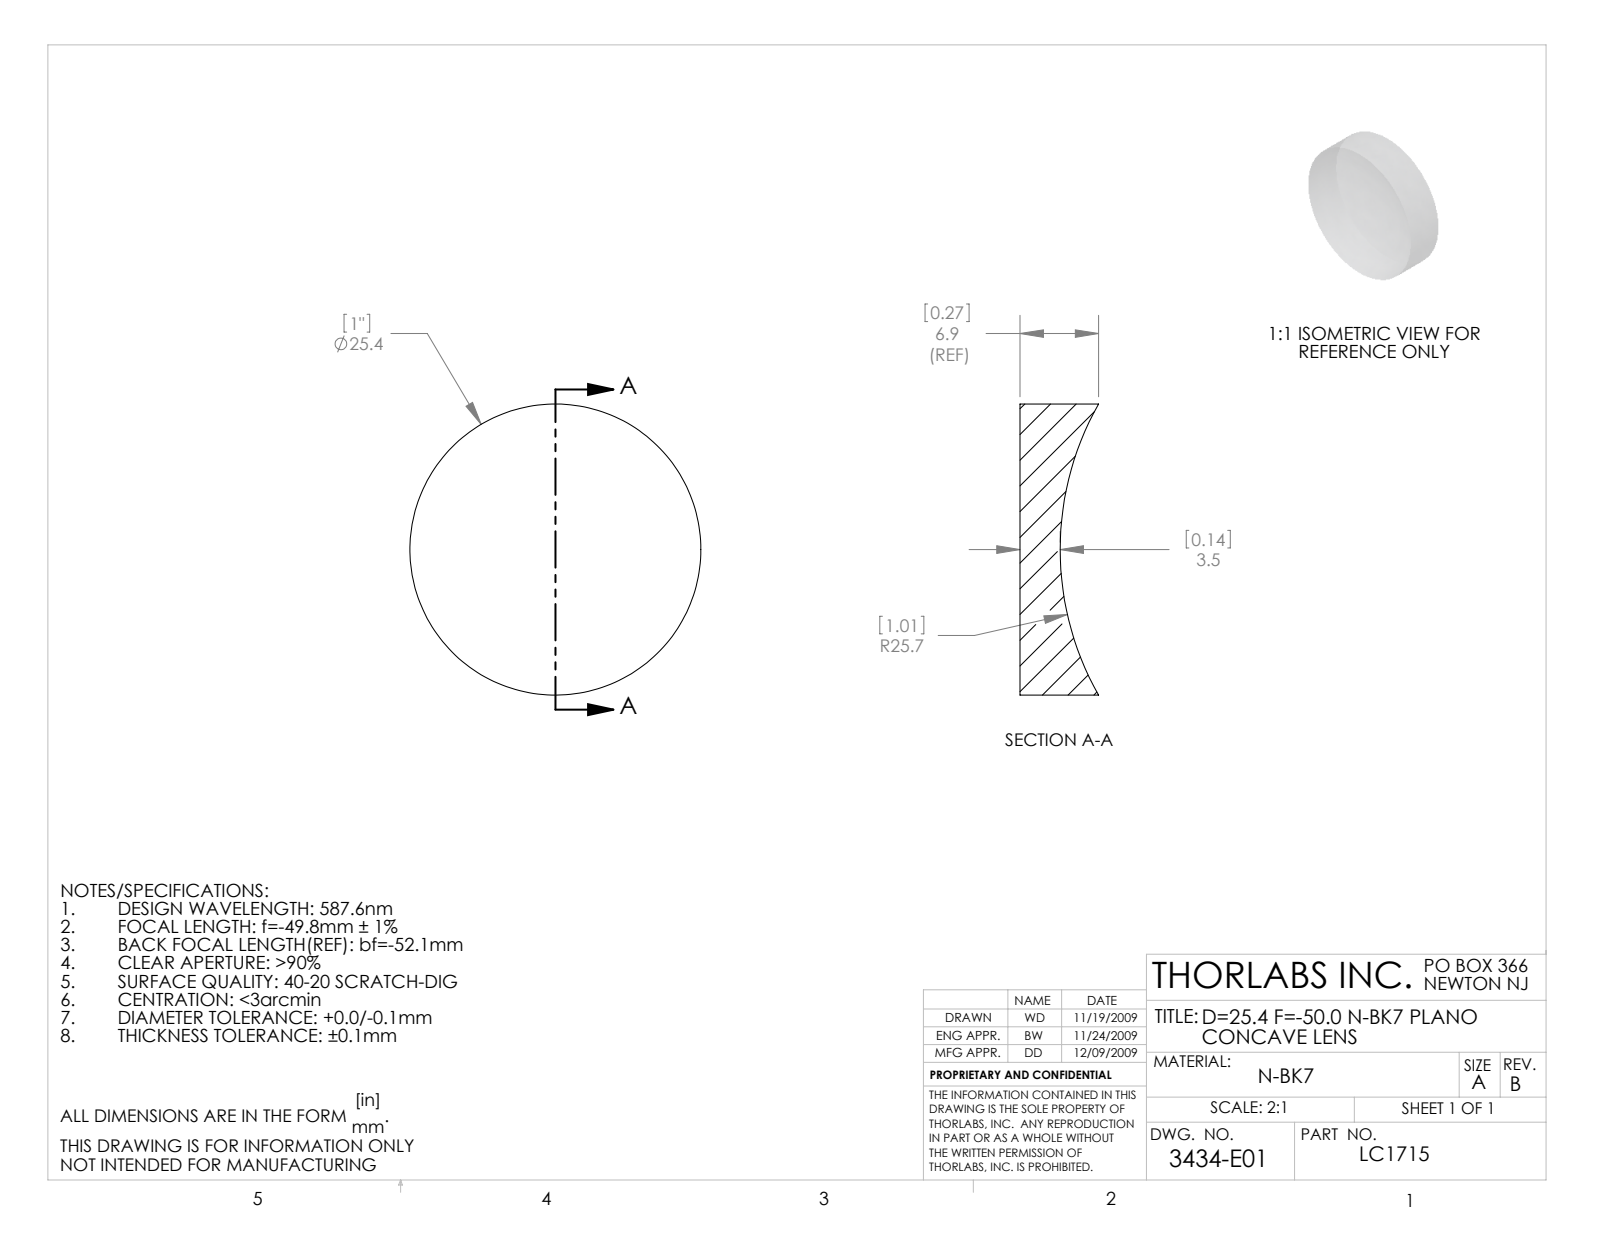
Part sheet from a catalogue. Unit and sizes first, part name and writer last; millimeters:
Units: millimetres
Overall size (bounding box): 25.4 × 25.4 × 6.85
Round bosses / shafts (diameter × count): ⌀25.4 ×1
Volume: 2 603 mm³ · Surface area: 1 596 mm²
Bodies: 1 solid, 5 faces (1 planar, 2 cylindrical, 2 other)
Part name (STEP PRODUCT): 3434-E0W
STEP written by: SolidWorks 2009 (AUTOMOTIVE_DESIGN)
